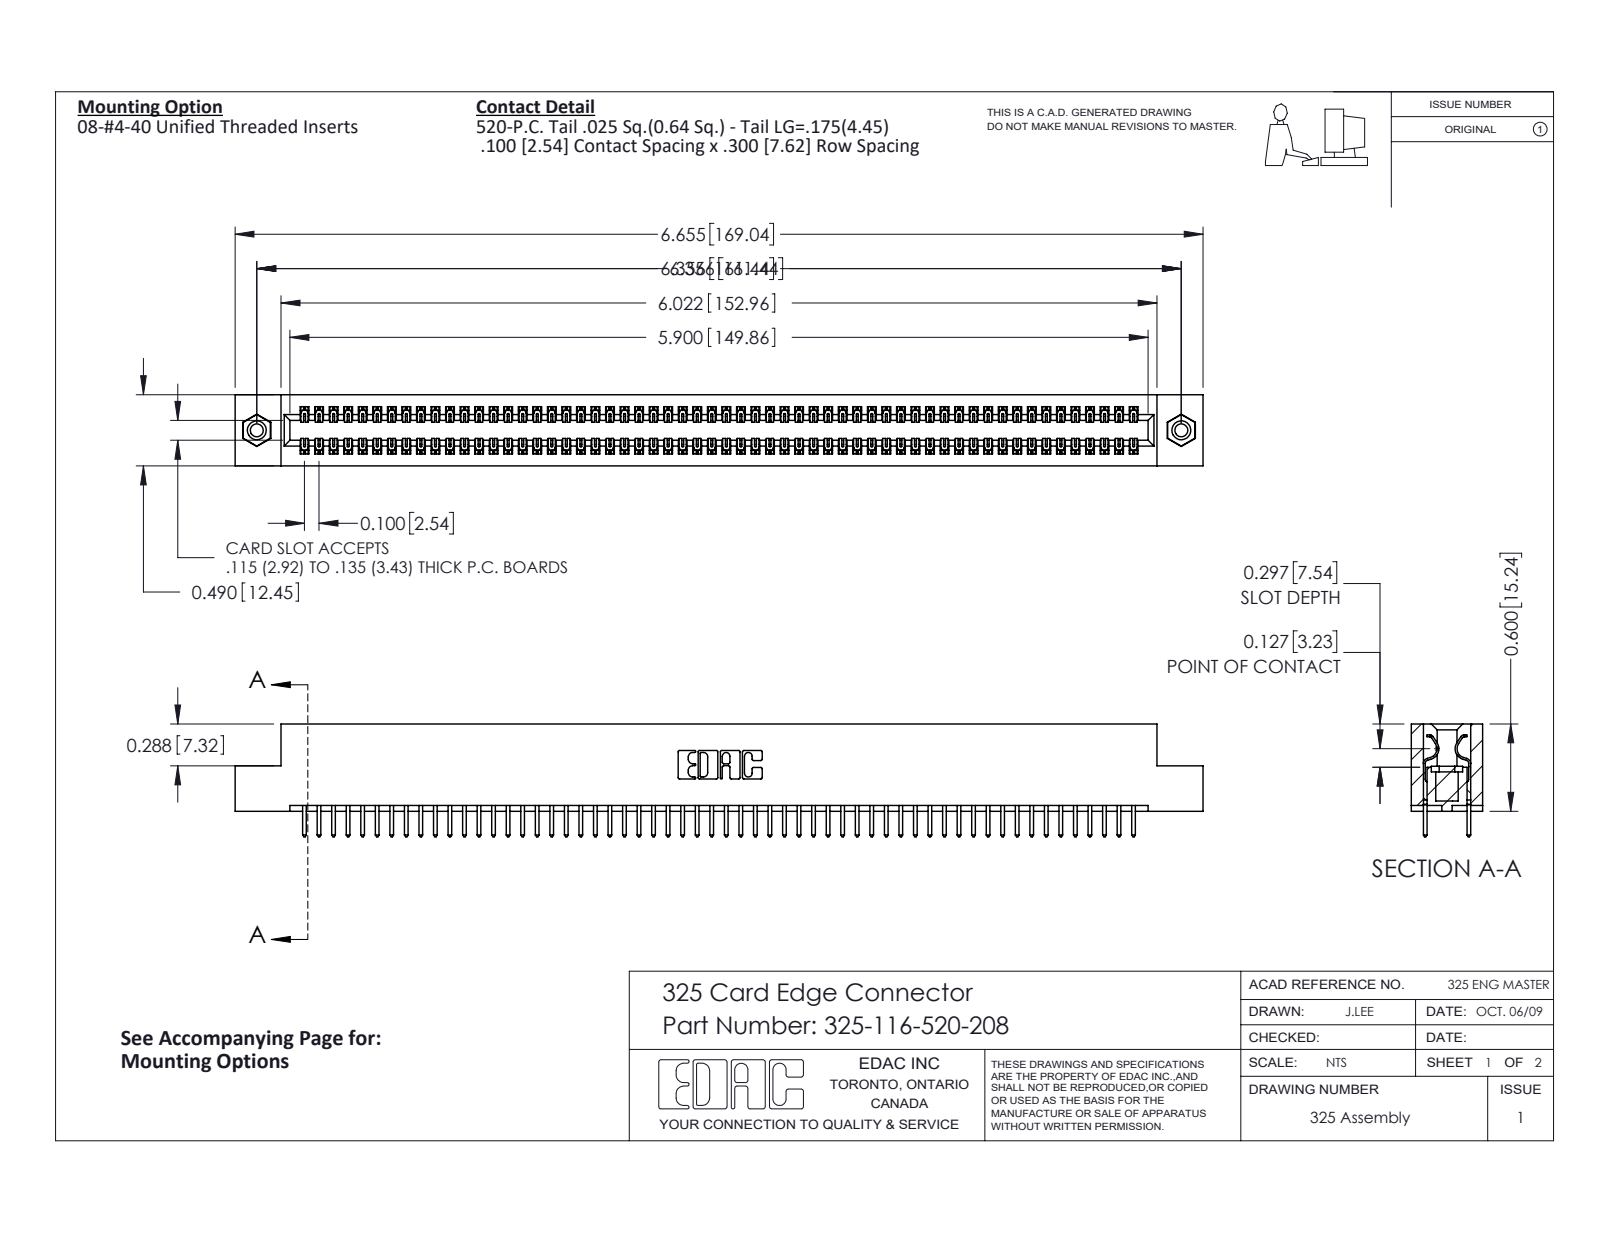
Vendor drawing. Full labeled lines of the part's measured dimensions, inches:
Part name (STEP PRODUCT): 345-250-001_345-250-003-102; 325 Part_TI; 325-116-520-208; 325-292-001_325-293-120
STEP written by: SolidWorks 2016 (CONFIG_CONTROL_DESIGN)
Units: inches
Bodies: 119 solids, 6206 faces (4278 planar, 1912 cylindrical, 16 other)
Overall size (bounding box): 6.655 × 0.775 × 0.49
Volume: 1.339 in³ · Surface area: 41.41 in²
Round holes (diameter × count): ⌀0.089 ×2, ⌀0.125 ×2, ⌀0.16 ×2
Round bosses / shafts (diameter × count): ⌀0.155 ×2
Partial cylindrical surfaces — rounded edges, fillets, slot ends (radius × count): R0.006 ×174, R0.01 ×116, R0.01 ×22, R0.007 ×6, R0.031 ×6, R0.026 ×3, R0.014 ×2, R0.022 ×2
Main face-to-face distances: 0.083, 0.407, 0.49, 0.107, 0.383, 0.025, 0.3, 0.325, 0.275, 0.263
Hole centre spacings: 6.356
